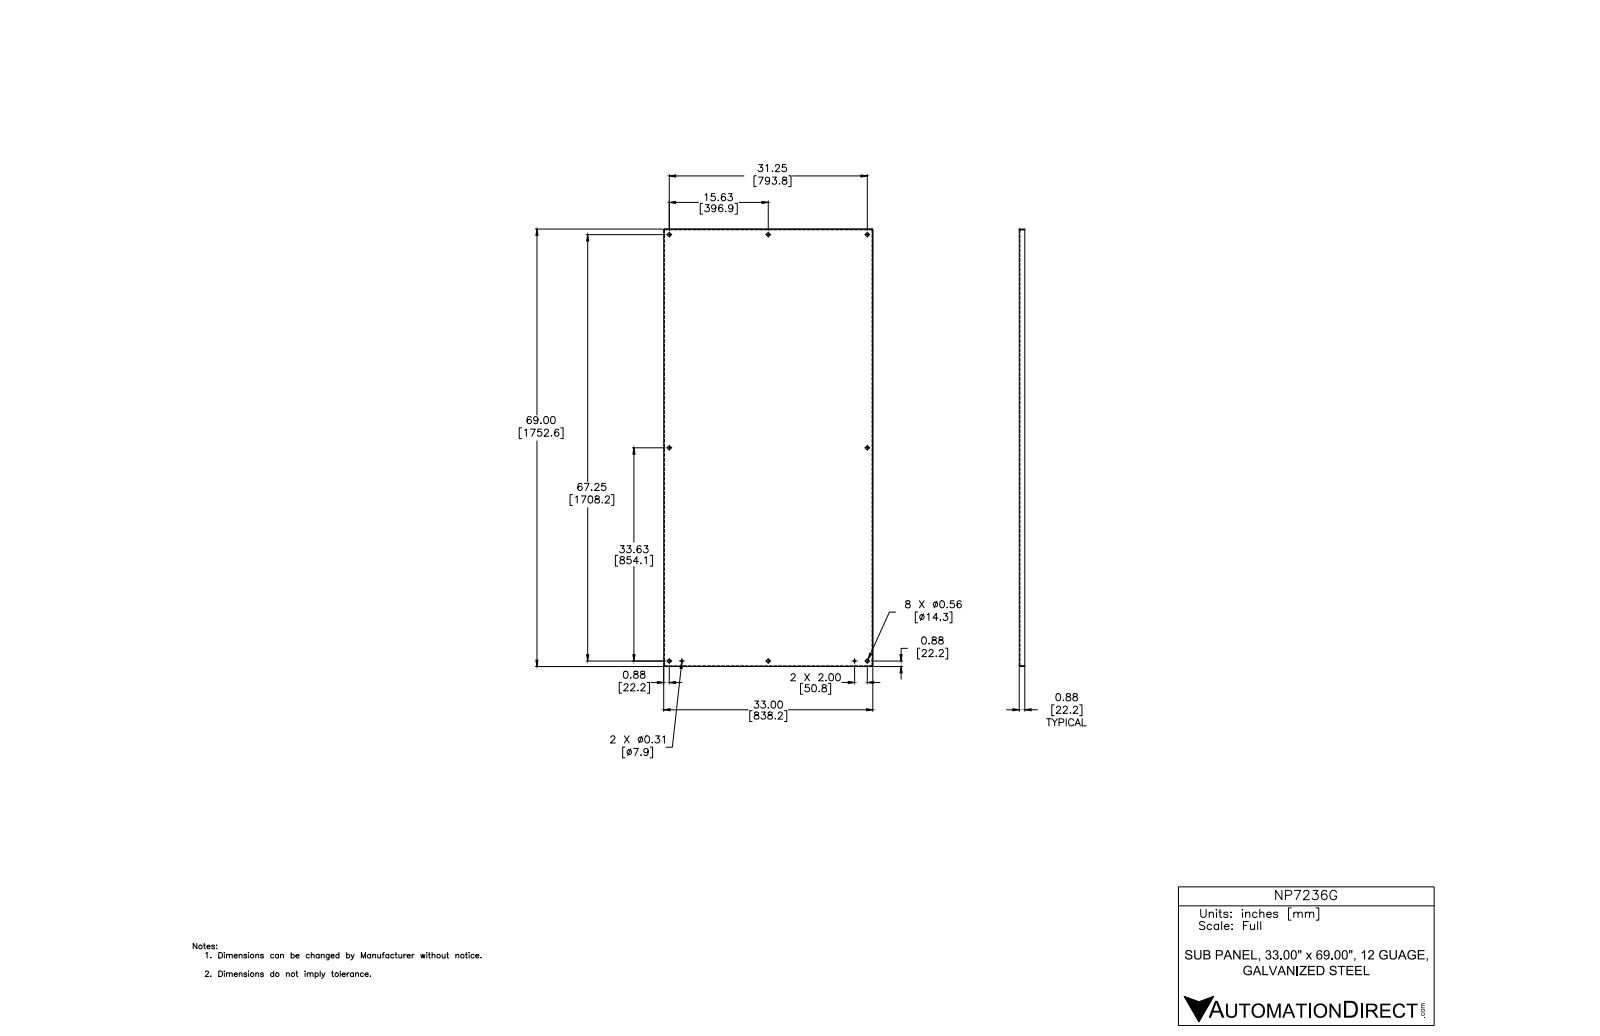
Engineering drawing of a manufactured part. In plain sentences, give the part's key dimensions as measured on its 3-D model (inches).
The part is named "NP7236G". Its 3-D file was written by "Autodesk Inventor 2012 (AUTOMOTIVE_DESIGN)". It is 1 solid with 48 faces: 22 planar, 18 cylindrical and 8 other. Overall it measures 69 by 33 by 0.875 inches. Its volume is 227.4 cubic inches and its surface area 4 875 square inches. Round holes: 8 of diameter 0.563, 2 of diameter 0.312. Partial cylindrical surfaces (rounded edges, fillets, slot ends): 4 of radius 0.031, 4 of radius 0.125. The main face-to-face distances are 0.094, 32.906, 33, 32.813, 68.906, 69, 68.813, 0.781, 0.875, 0.105. The hole center spacings are 33.625, 45.904, 69.042, 31.25, 67.25, 13.625, 15.625, 15.625.
